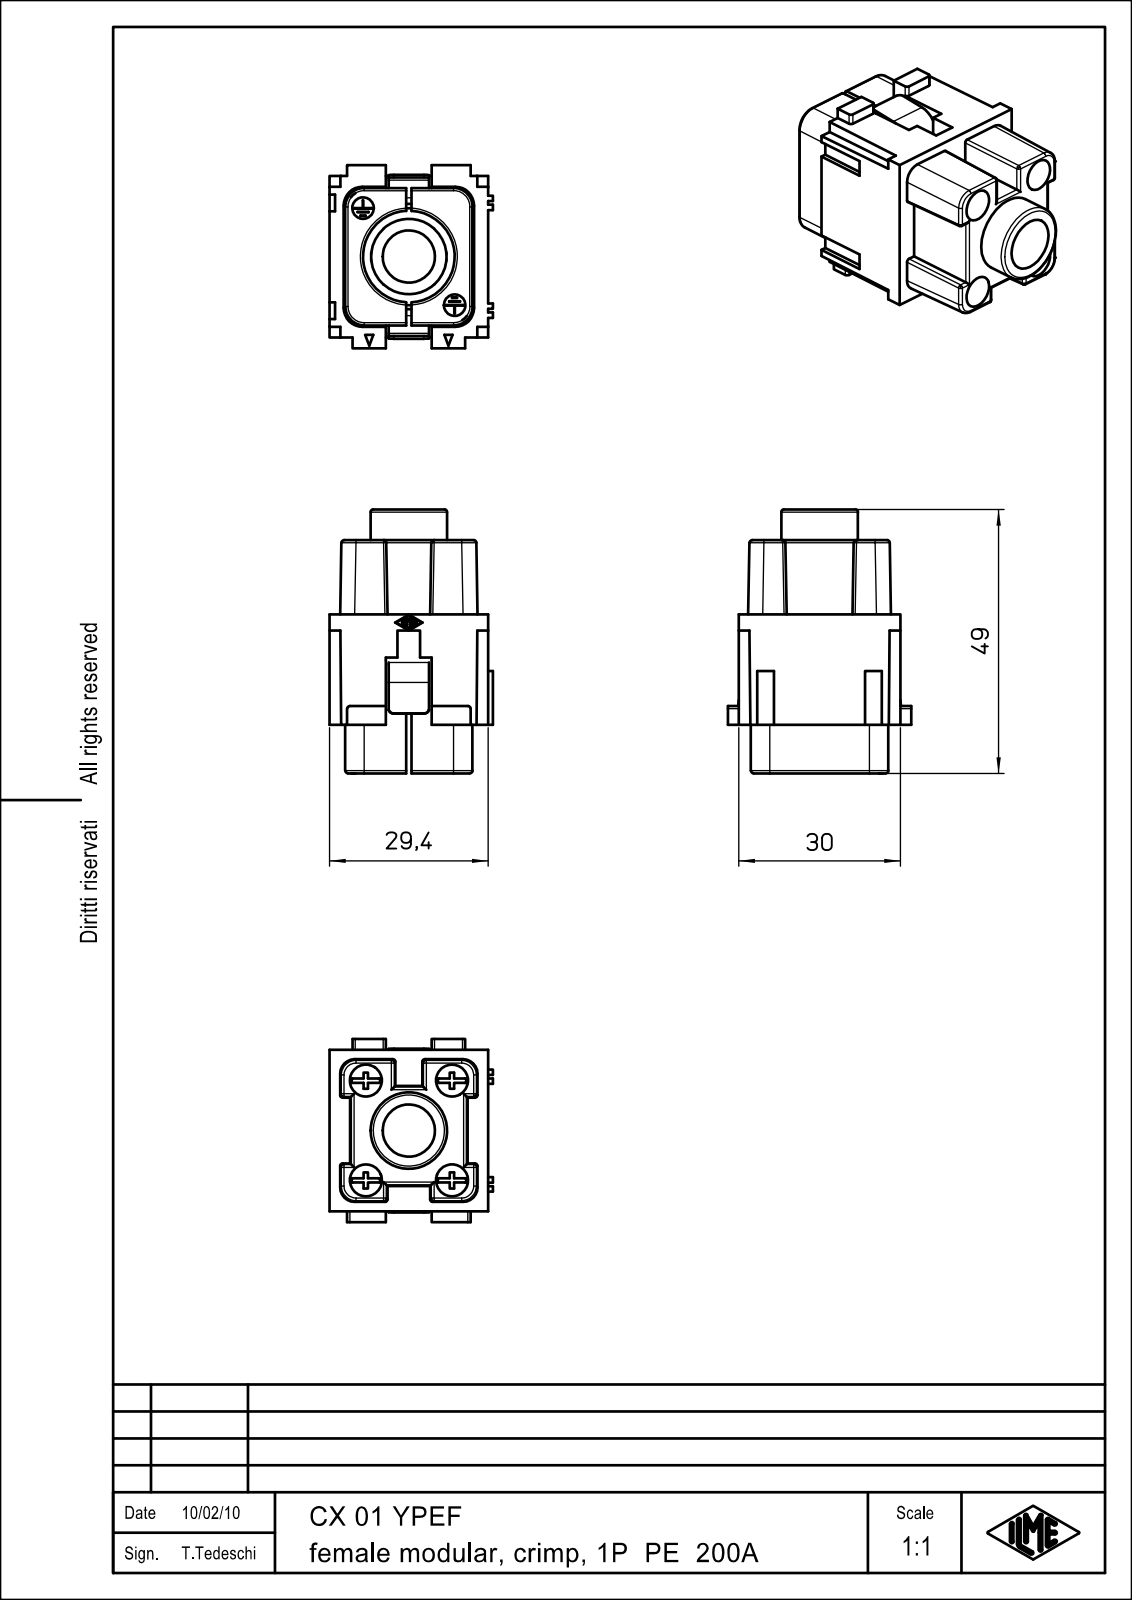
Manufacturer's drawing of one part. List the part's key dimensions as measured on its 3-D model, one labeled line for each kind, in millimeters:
Part name (STEP PRODUCT): CX_01_YPEF
STEP written by: CoCreate Modeling 16.00A 16-Aug-2008 (C) Parametric Technology GmbH (AUTOMOTIVE_DESIGN)
Units: millimetres
Bodies: 1 solid, 590 faces (302 planar, 179 cylindrical, 109 other)
Overall size (bounding box): 49 × 34 × 30.3
Volume: 19 933 mm³ · Surface area: 14 594 mm²
Round holes (diameter × count): ⌀2.46 ×4, ⌀2.8 ×4, ⌀3.2 ×4, ⌀4 ×2, ⌀9.7 ×1, ⌀14 ×1, ⌀17 ×1, ⌀19.6 ×1
Round bosses / shafts (diameter × count): ⌀5.5 ×4, ⌀3 ×4, ⌀2.55 ×4, ⌀3.8 ×2, ⌀14.2 ×1
Partial cylindrical surfaces — rounded edges, fillets, slot ends (radius × count): R0.5 ×32, R0.3 ×8, R3.5 ×8, R1 ×4, R2.7 ×4, R3.6 ×4, R2 ×2, R4.1 ×2
Main face-to-face distances: 26.5, 2.9, 9, 2.25, 27.75, 29.4, 14.2, 8.5, 15.2, 1
Hole centre spacings: 12.23, 0.56, 12.38, 16, 16.5, 18.26, 18.5, 24.46
